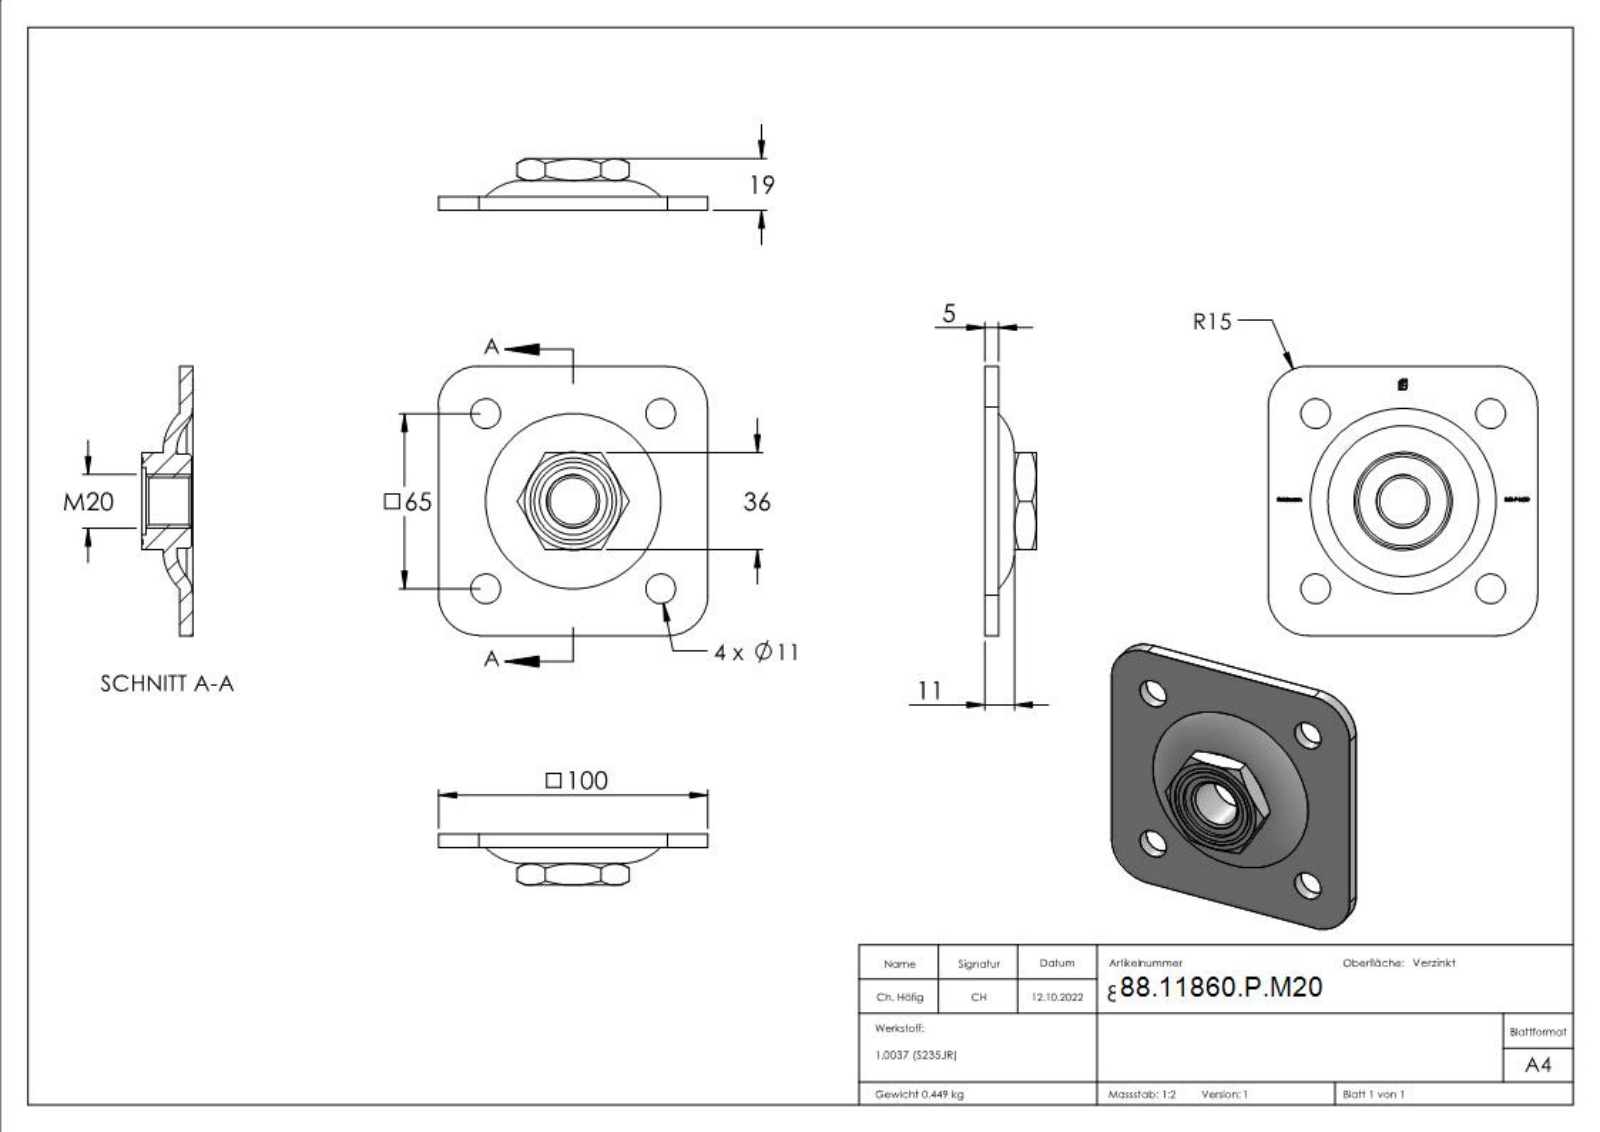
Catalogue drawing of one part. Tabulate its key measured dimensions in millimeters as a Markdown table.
| quantity | value |
| --- | --- |
| part name | 860-P-M20 |
| STEP written by | SolidWorks 2018 (CONFIG_CONTROL_DESIGN) |
| units | millimeters |
| bodies | 1 solid, 315 faces (160 planar, 13 cylindrical, 142 other) |
| overall size | 100 × 100 × 19 |
| volume | 57 503 mm³ |
| surface area | 24 182 mm² |
| round holes (diameter × count) | 11 × 4, 17.5 × 1, 25 × 1, 32 × 1 |
| round bosses / shafts (diameter × count) | 35 × 1, 29 × 1 |
| partial cylindrical surfaces (radius × count) | 15 × 4 |
| main face-to-face distances | 5, 100, 4.5, 0.5, 36, 19, 18.5, 14, 32, 68 |
| hole center spacings | 45.96, 65, 91.92 |
